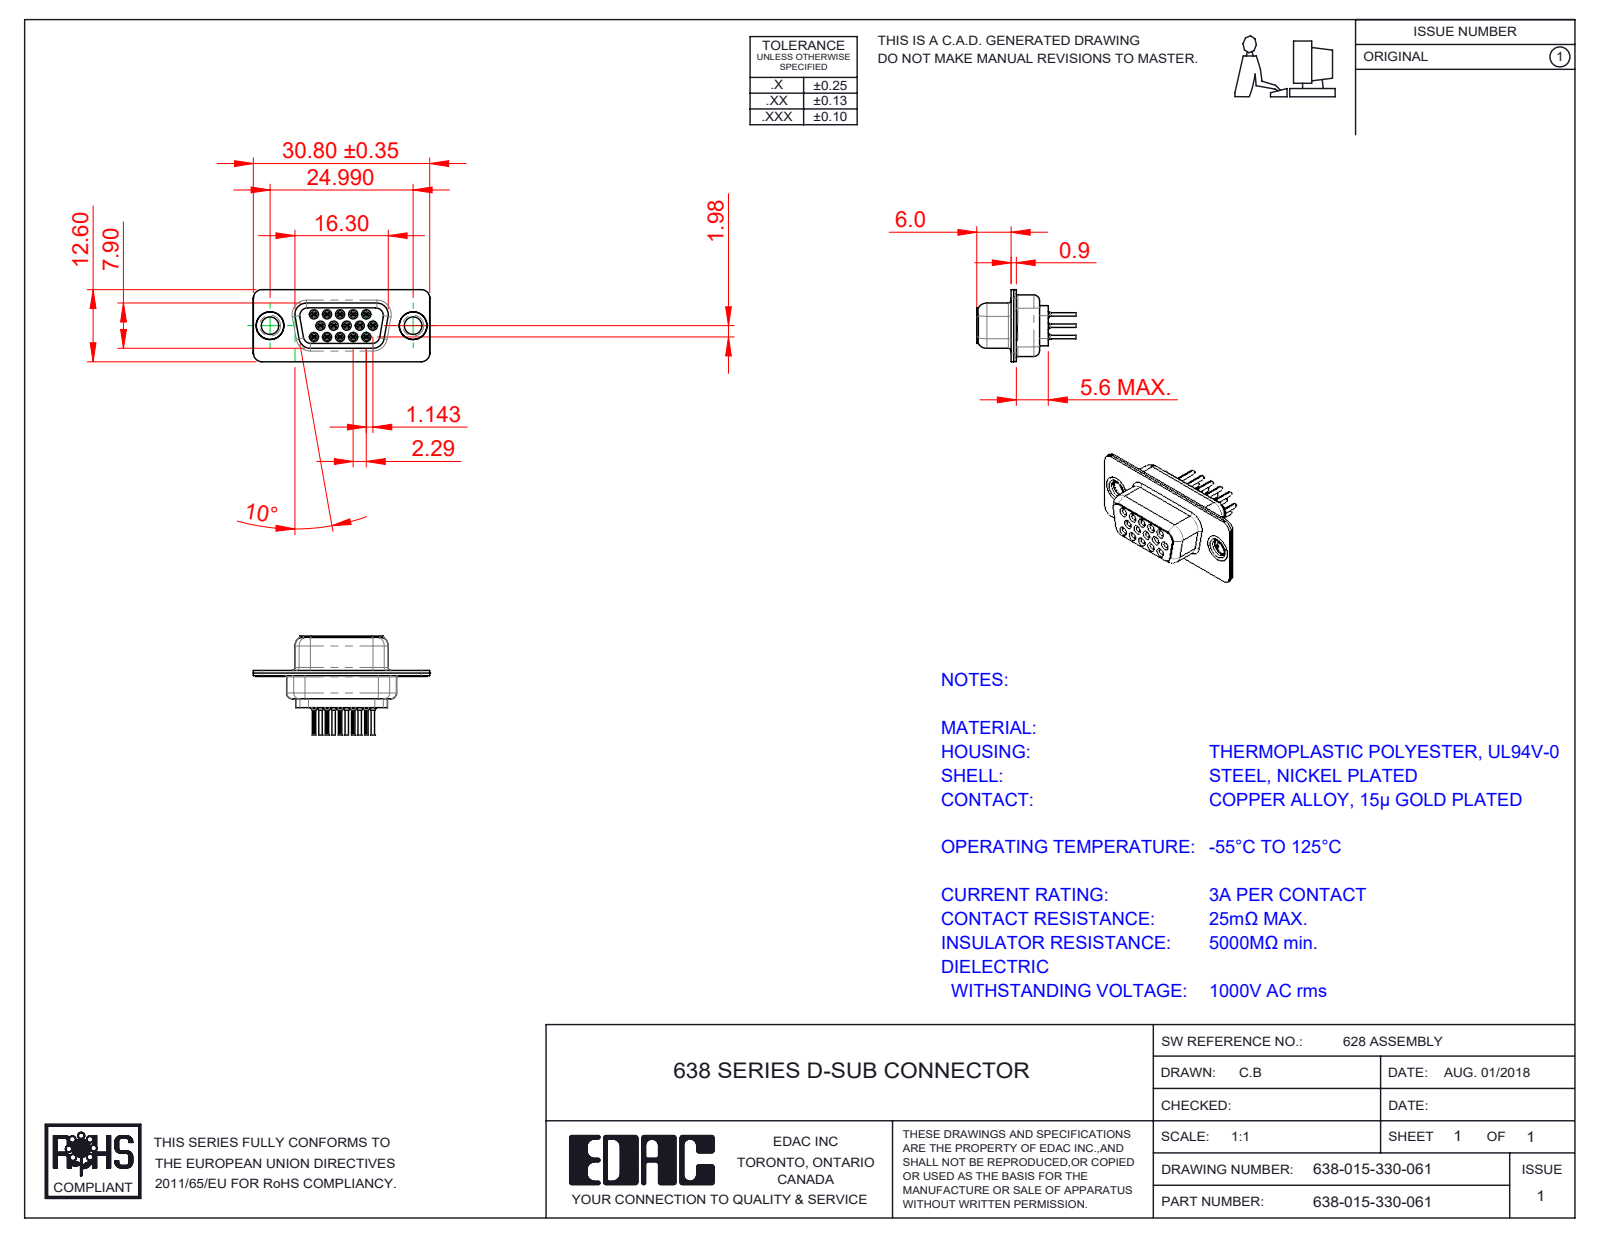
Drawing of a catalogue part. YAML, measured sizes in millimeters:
part_name: "638 Housing_15 Contacts; 638 Contact Row 3_30; 638 Shell Rear_15 Contacts; 638 Contact Row 2_30 (+4 more)"
step_written_by: "SolidWorks 2020 (CONFIG_CONTROL_DESIGN)"
units: millimeters
bodies: {solids: 20, faces: 2158, planar: 532, cylindrical: 616, other: 1010}
overall_size: [30.81, 17.3, 12.6]
volume: 1498
surface_area: 5452
round_holes:
  - {diameter: 0.2, count: 15}
  - {diameter: 0.8, count: 15}
  - {diameter: 1, count: 15}
  - {diameter: 1.1, count: 15}
  - {diameter: 1.6, count: 15}
  - {diameter: 1.7, count: 15}
  - {diameter: 1.8, count: 15}
  - {diameter: 2, count: 2}
  - {diameter: 3.05, count: 2}
  - {diameter: 4, count: 2}
  - {diameter: 4.05, count: 2}
  - {diameter: 4.85, count: 2}
round_bosses_or_shafts:
  - {diameter: 2, count: 15}
  - {diameter: 1.5, count: 15}
  - {diameter: 1.2, count: 15}
  - {diameter: 0.6, count: 15}
  - {diameter: 5, count: 2}
  - {diameter: 4.95, count: 2}
  - {diameter: 4.8, count: 2}
  - {diameter: 3.55, count: 2}
partial_cylinders:
  - {radius: 0.1, count: 30}
  - {radius: 1.5, count: 20}
  - {radius: 2, count: 12}
  - {radius: 0.28, count: 10}
  - {radius: 1.55, count: 8}
  - {radius: 1.35, count: 5}
  - {radius: 0.25, count: 4}
  - {radius: 0.5, count: 4}
face_to_face_distances: [0.45, 0.9, 0.4, 1.43, 8.88, 6.6, 1.4, 2.28, 7.05, 6.05]
hole_center_spacings: [3.96, 2.28, 4.57, 2.29, 6.05, 6.04, 6.86, 7.92]
